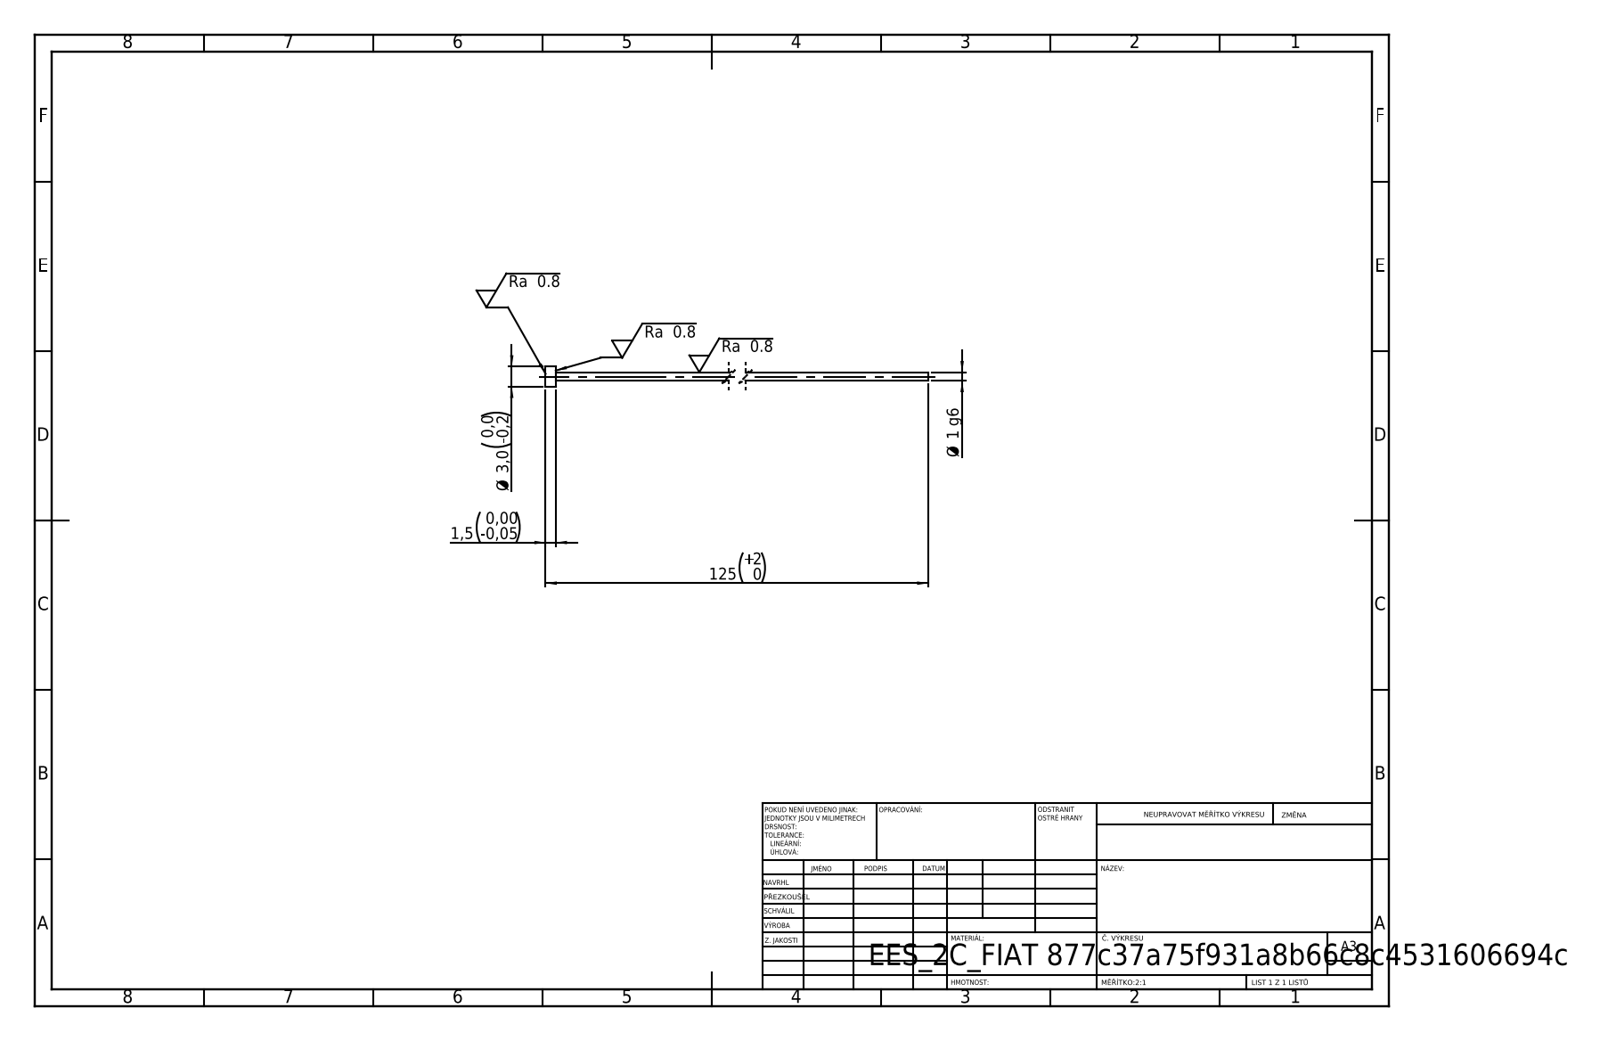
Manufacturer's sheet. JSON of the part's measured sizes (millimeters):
{"step_written_by": "SolidWorks 2019 (CONFIG_CONTROL_DESIGN)", "units": "millimeters", "bodies": {"solids": 1, "faces": 7, "planar": 3, "cylindrical": 4, "other": 0}, "overall_size": [125, 3, 3], "volume_mm3": 175, "surface_area_mm2": 533, "round_bosses_or_shafts": [[3, 1], [1.3, 1]], "face_to_face_distances": [1.5, 125, 123.5]}
